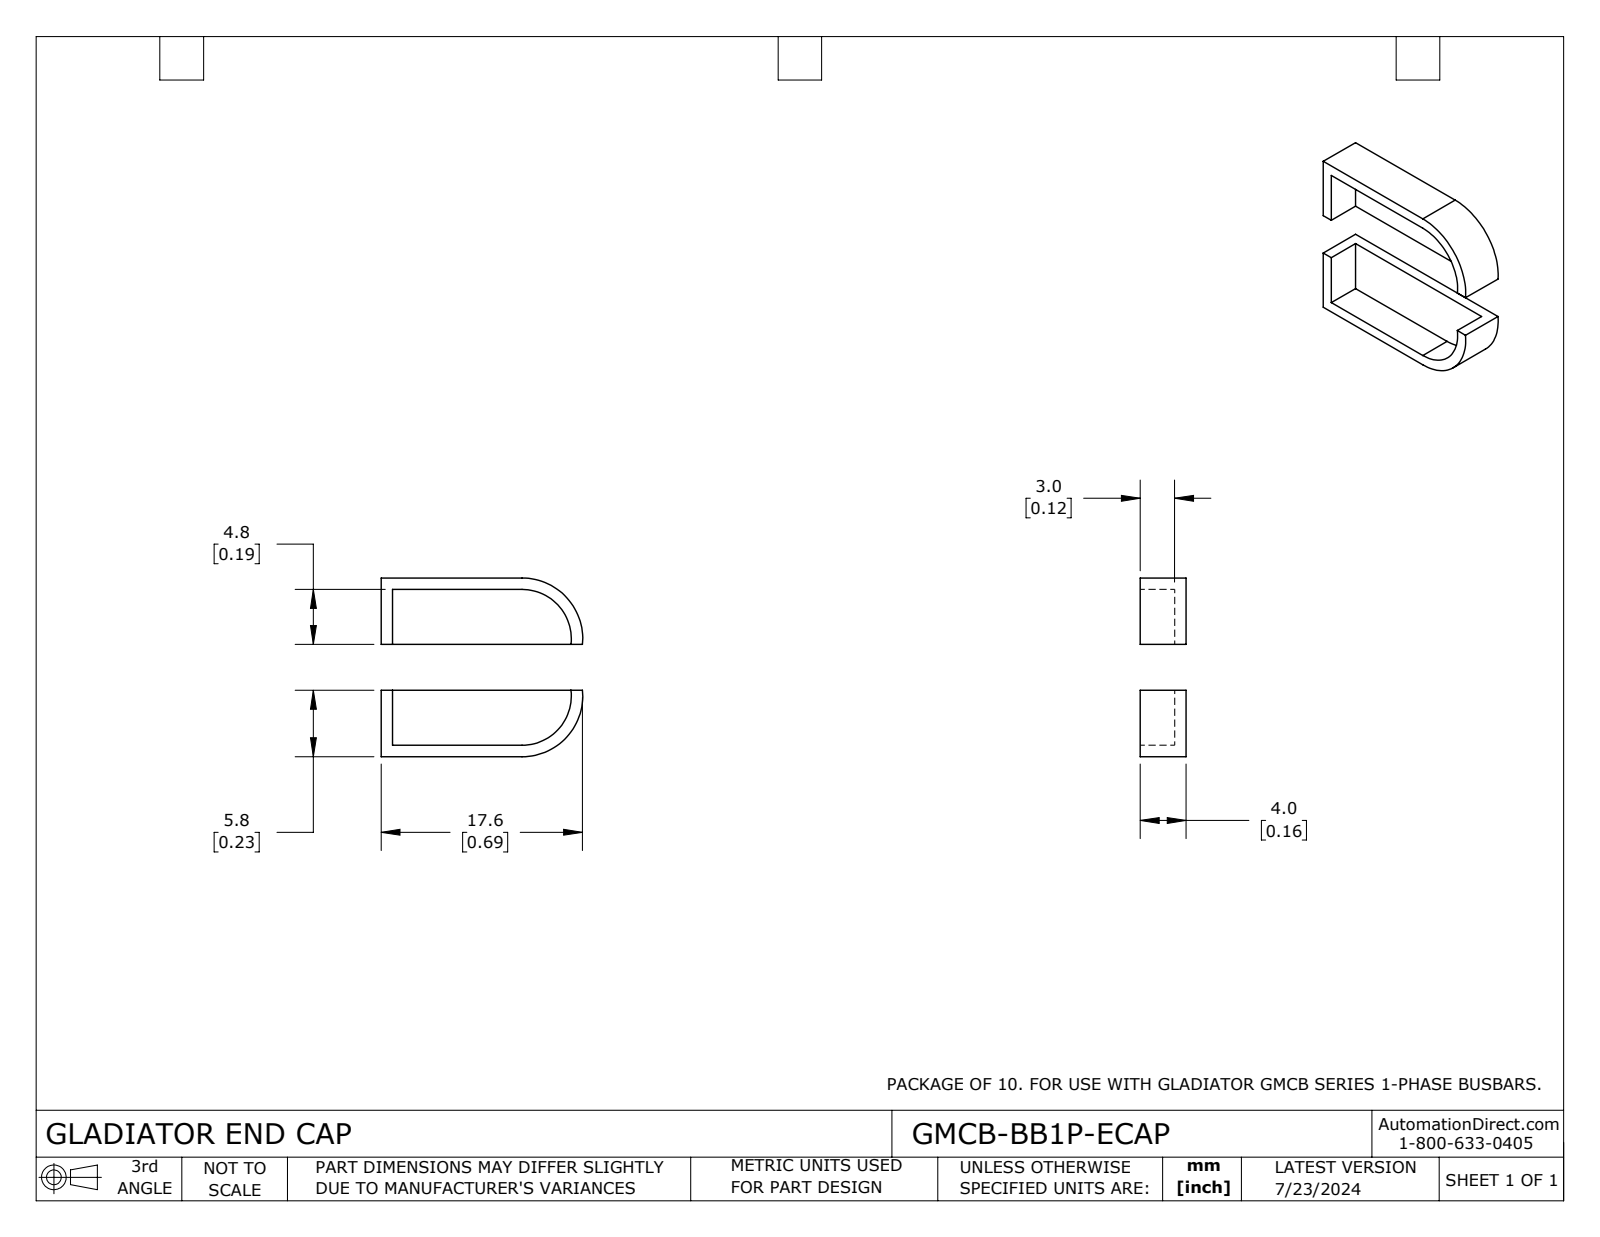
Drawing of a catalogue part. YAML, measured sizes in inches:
part_name: "GMCB-BB1P-ECAP"
step_written_by: "SolidWorks 2023 (CONFIG_CONTROL_DESIGN)"
units: inches
bodies: {solids: 2, faces: 22, planar: 16, cylindrical: 6, other: 0}
overall_size: [0.693, 0.614, 0.157]
volume: 0.021
surface_area: 1.22
partial_cylinders:
  - {radius: 0.169, count: 2}
  - {radius: 0.209, count: 2}
face_to_face_distances: [0.039, 0.157, 0.575, 0.118, 0.614, 0.228, 0.386, 0.189, 0.346, 0.535]
